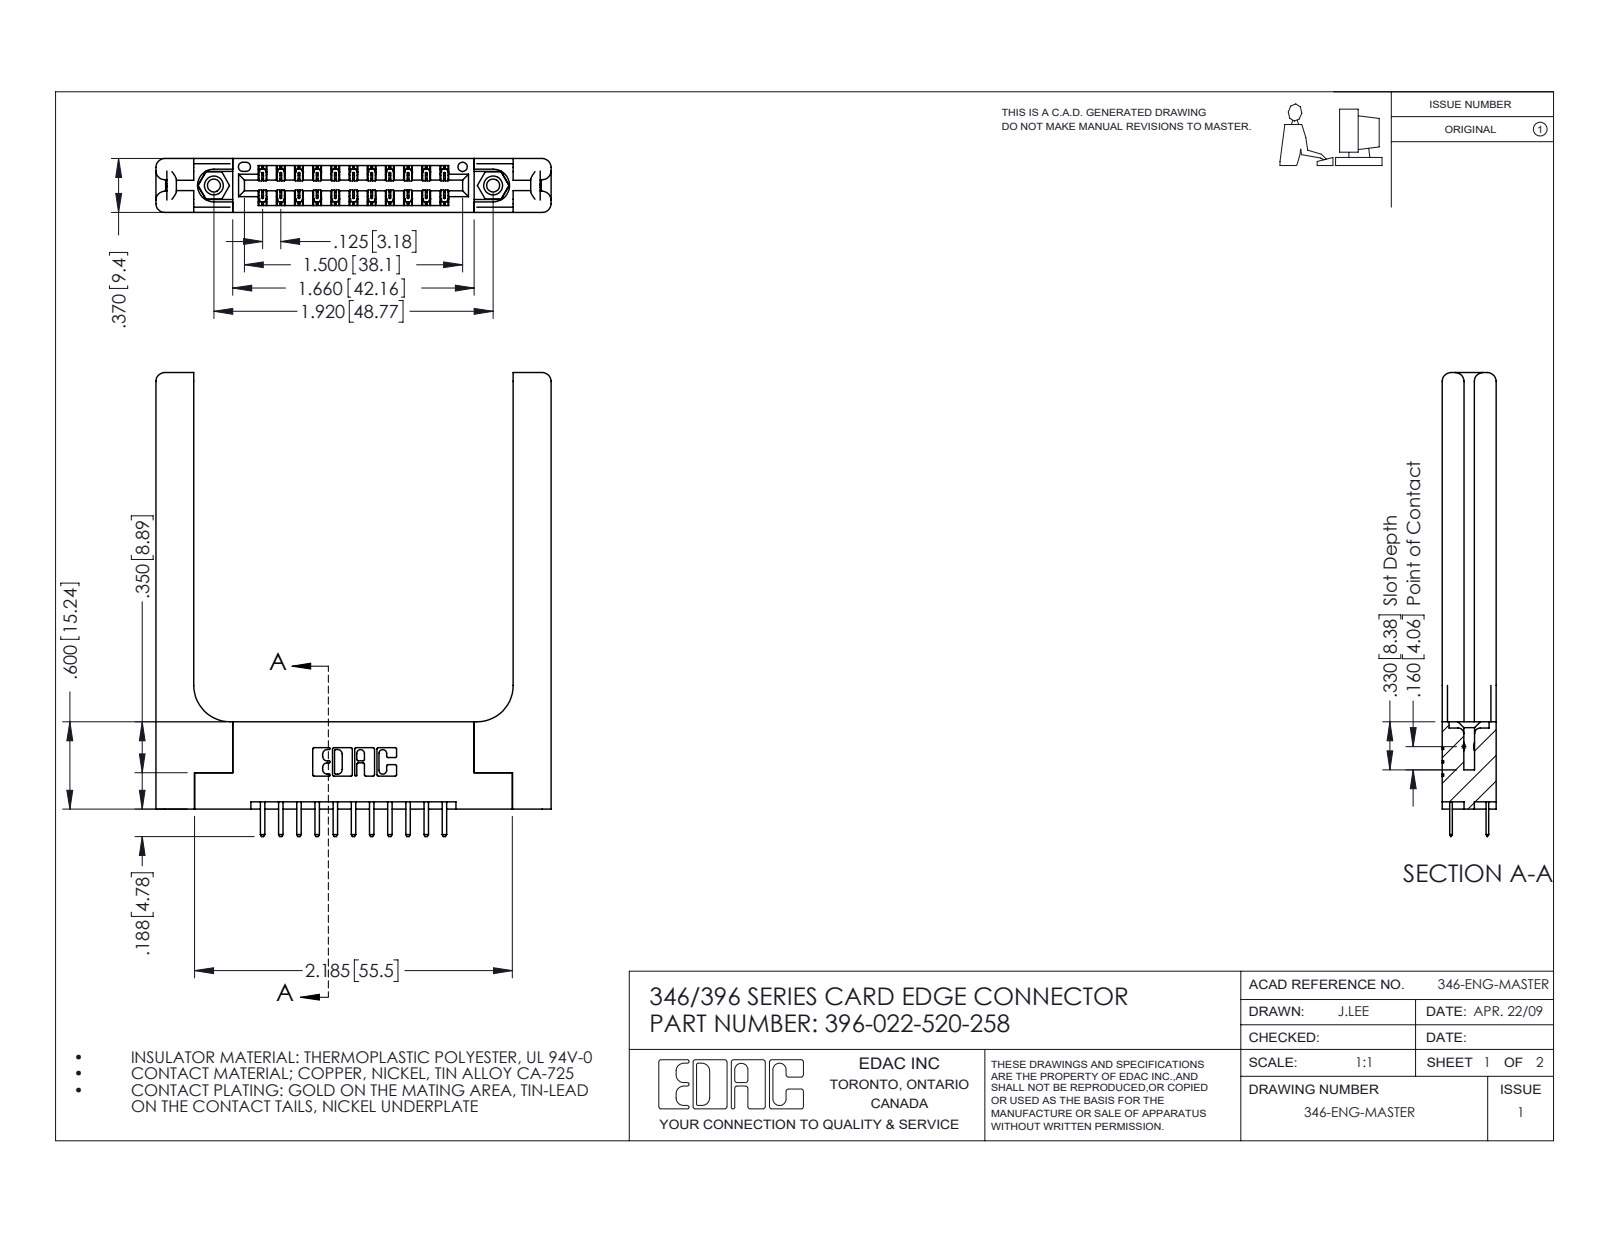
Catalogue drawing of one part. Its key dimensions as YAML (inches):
part_name: "346-220-058_345-220-058; 346 Part_Flush Mounting Lugs - 0.156 Dia-TH; 396-022-520-258; 345-250-001_345-250-001-102 (+1 more)"
step_written_by: "SolidWorks 2016 (CONFIG_CONTROL_DESIGN)"
units: inches
bodies: {solids: 27, faces: 1610, planar: 1038, cylindrical: 512, other: 60}
overall_size: [3.188, 2.716, 0.37]
volume: 0.853
surface_area: 20.72
round_holes:
  - {diameter: 0.089, count: 2}
  - {diameter: 0.125, count: 2}
  - {diameter: 0.156, count: 2}
  - {diameter: 0.064, count: 1}
round_bosses_or_shafts:
  - {diameter: 0.155, count: 2}
partial_cylinders:
  - {radius: 0.006, count: 33}
  - {radius: 0.01, count: 26}
  - {radius: 0.01, count: 22}
  - {radius: 0.06, count: 16}
  - {radius: 0.007, count: 6}
  - {radius: 0.031, count: 6}
  - {radius: 0.026, count: 3}
  - {radius: 0.014, count: 2}
face_to_face_distances: [0.37, 0.15, 0.072, 0.25, 0.148, 0.22, 0.102, 0.048, 0.322, 0.173]
hole_center_spacings: [0.246, 1.715, 1.92]
